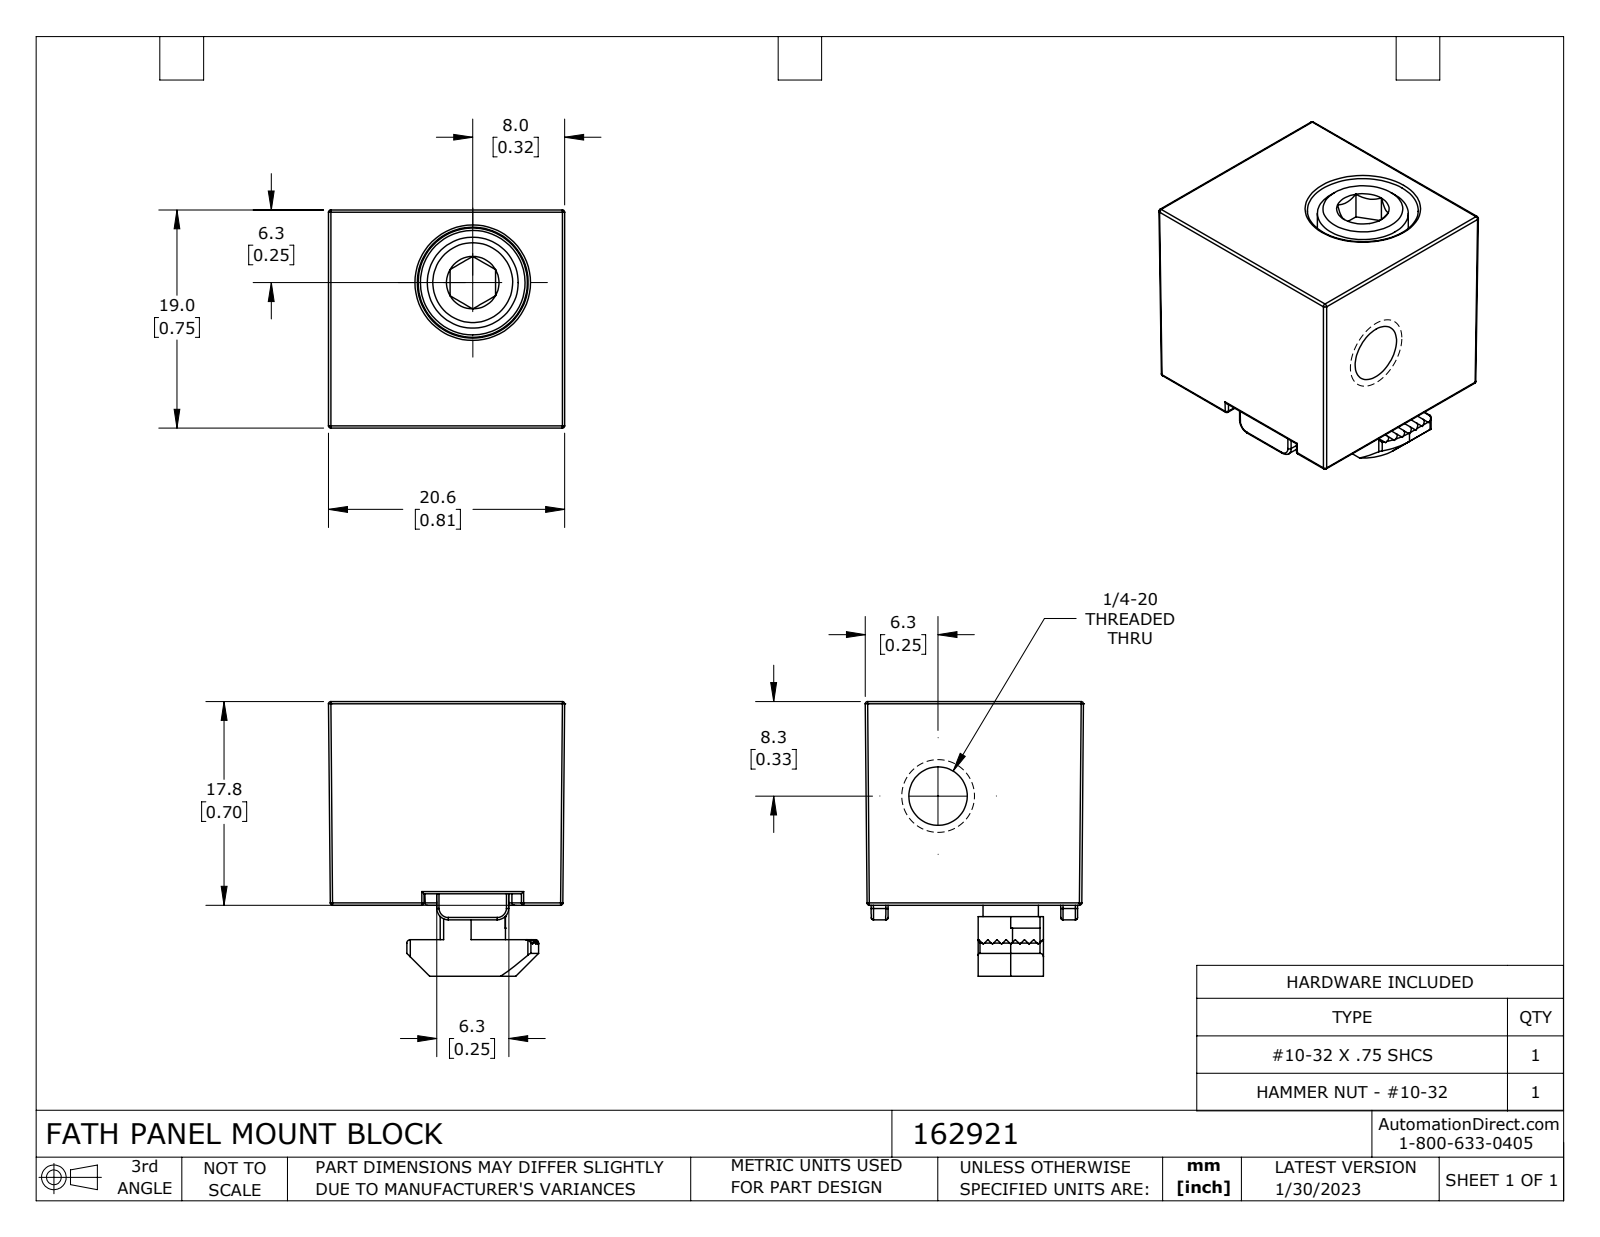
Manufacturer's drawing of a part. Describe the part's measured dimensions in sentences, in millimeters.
The part is named "162921". Its 3-D file was written by "SolidWorks 2021 (CONFIG_CONTROL_DESIGN)". It is 2 solids with 253 faces: 98 planar, 85 cylindrical and 70 other. Overall it measures 24 by 20.6 by 19.1 millimeters. Its volume is 5 670 cubic millimeters and its surface area 4 159 square millimeters. Round holes: 1 of diameter 4, 1 of diameter 5.1. Round bosses or shafts: 1 of diameter 8, 1 of diameter 4.8. Partial cylindrical surfaces (rounded edges, fillets, slot ends): 43 of radius 0.2, 8 of radius 0.3, 3 of radius 2.1, 2 of radius 1, 2 of radius 3, 1 of radius 4.5, 1 of radius 5.7. The main face-to-face distances are 17.8, 10.2, 4.8, 14.7, 5.7, 2, 7.8, 1, 11.9, 6.2.
